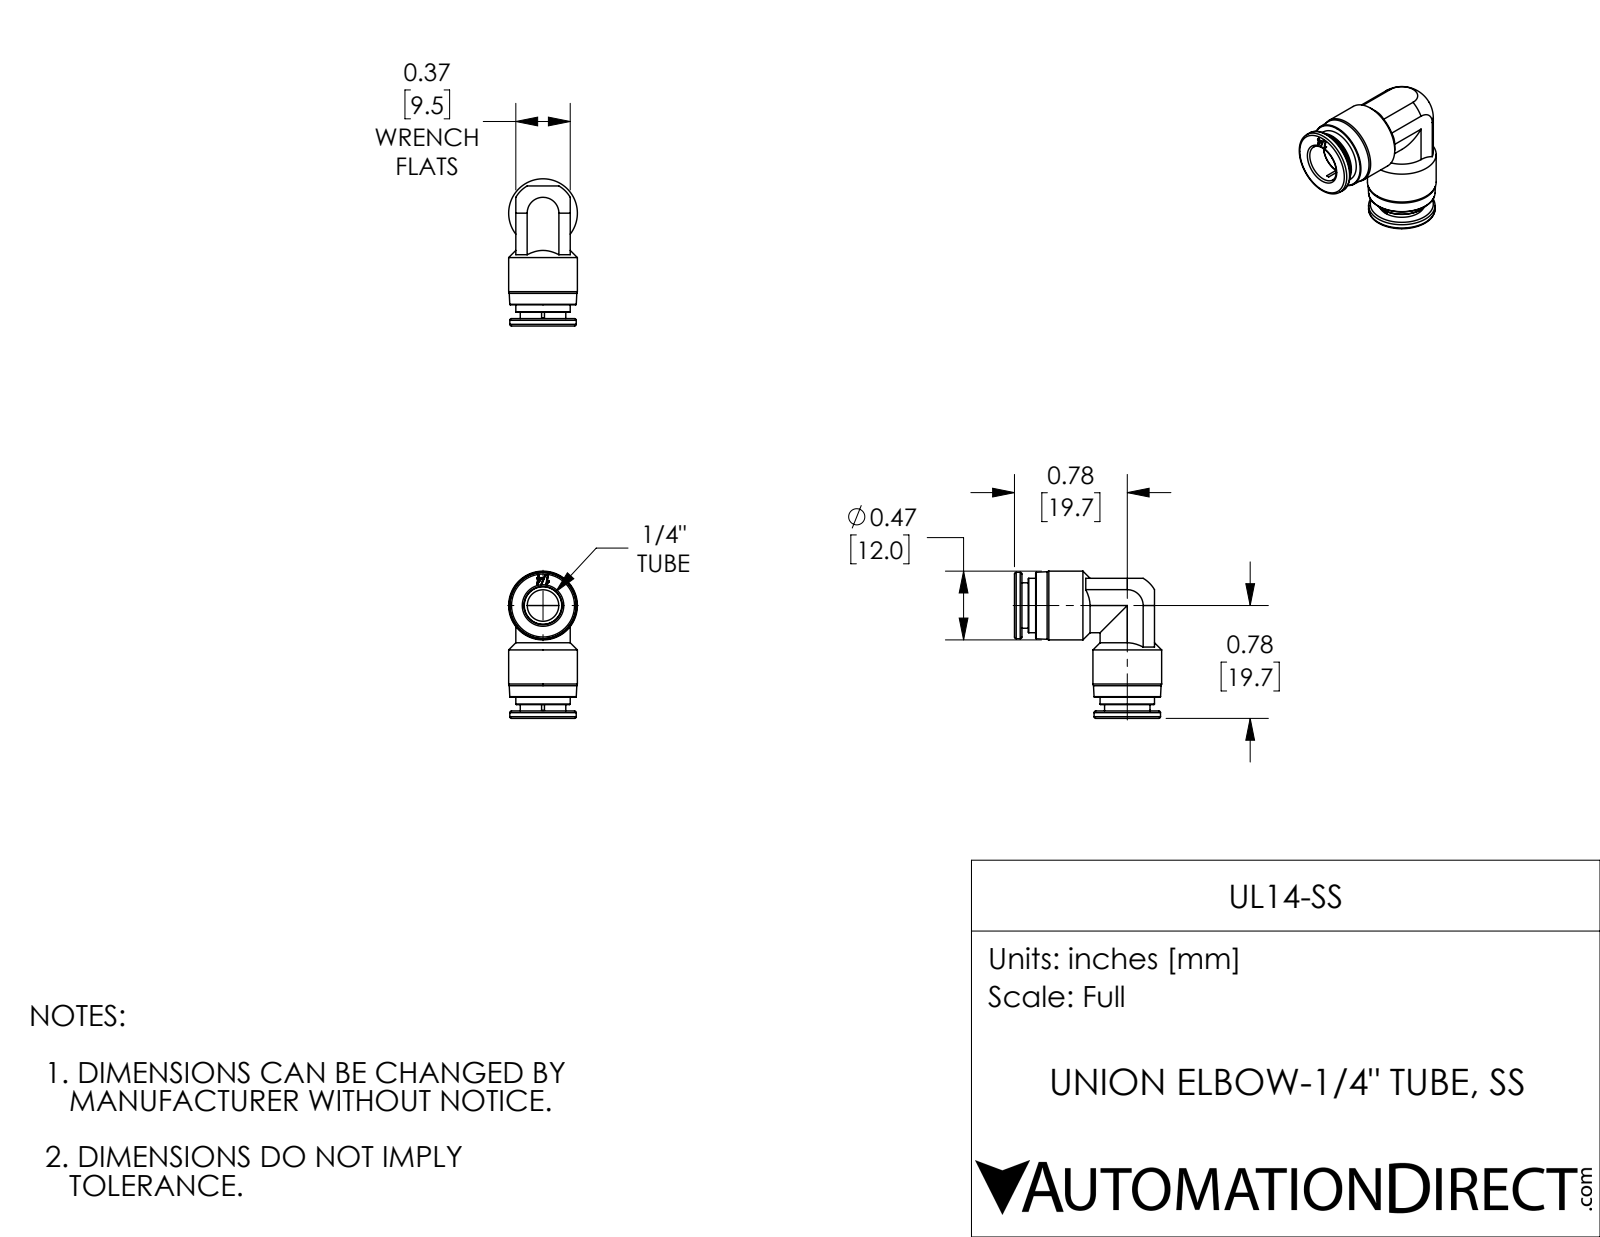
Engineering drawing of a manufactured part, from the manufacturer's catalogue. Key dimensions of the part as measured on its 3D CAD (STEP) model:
Part name (STEP PRODUCT): UL14-SS
STEP written by: SolidWorks 2017 (AUTOMOTIVE_DESIGN)
Units: inches
Bodies: 1 solid, 168 faces (82 planar, 39 cylindrical, 47 other)
Overall size (bounding box): 1.012 × 1.012 × 0.472
Volume: 0.146 in³ · Surface area: 4.097 in²
Round holes (diameter × count): ⌀0.217 ×2, ⌀0.258 ×2, ⌀0.262 ×2, ⌀0.319 ×2
Round bosses / shafts (diameter × count): ⌀0.472 ×2, ⌀0.457 ×2, ⌀0.374 ×2, ⌀0.313 ×2
Partial cylindrical surfaces — rounded edges, fillets, slot ends (radius × count): R0.217 ×2
Main face-to-face distances: 0.051, 0.963, 0.911, 0.094, 0.146, 0.817, 0.374, 0.622, 0.571, 0.476
